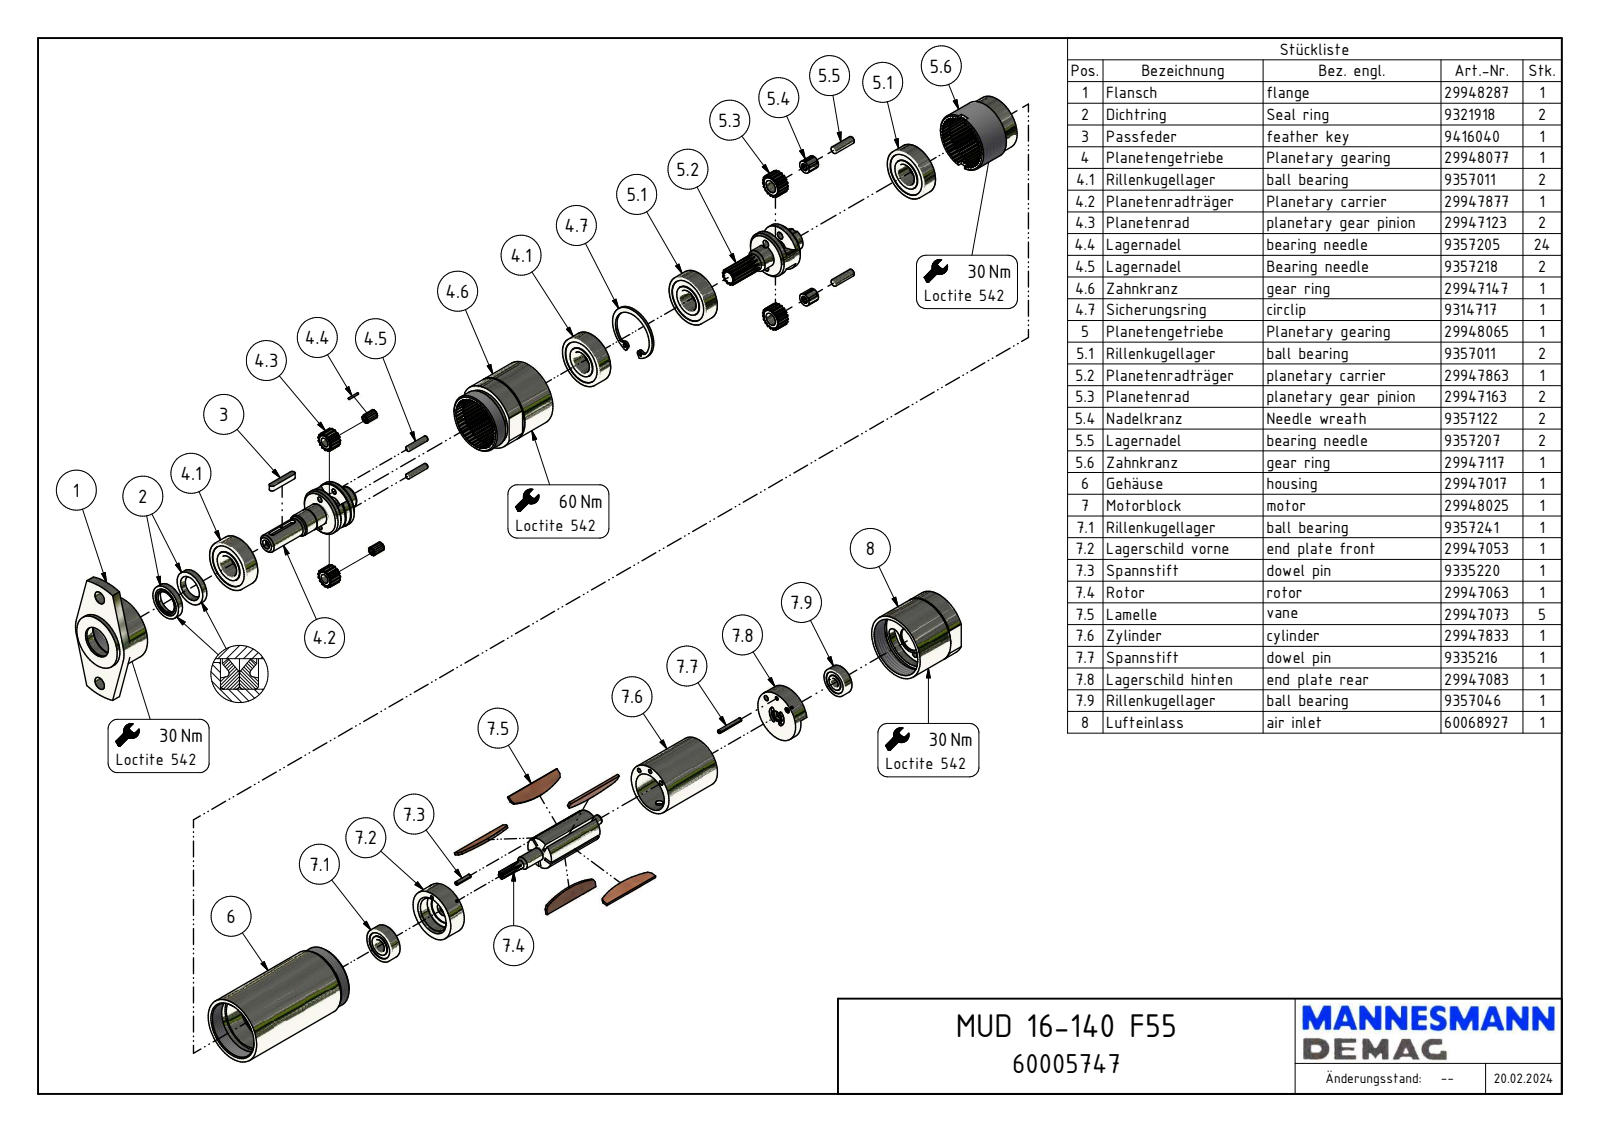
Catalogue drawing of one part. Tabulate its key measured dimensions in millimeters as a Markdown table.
| quantity | value |
| --- | --- |
| part name | MUD 16-140 F55_60005747 |
| STEP written by | Autodesk Inventor 2024 (AUTOMOTIVE_DESIGN) |
| units | millimeters |
| bodies | 1 solid, 139 faces (91 planar, 25 cylindrical, 23 other) |
| overall size | 169.7 × 70 × 36 |
| volume | 150 527 mm³ |
| surface area | 22 719 mm² |
| round holes (diameter × count) | 7 × 2, 8.57 × 2, 3.24 × 1, 11.45 × 1, 17 × 1 |
| round bosses / shafts (diameter × count) | 36 × 1, 34.99 × 1, 30 × 1, 11.95 × 1, 10 × 1, 9.8 × 1 |
| partial cylindrical surfaces (radius × count) | 1.5 × 2, 35 × 1 |
| main face-to-face distances | 5, 143.2, 138.2, 2, 7, 145.2, 33, 135.7, 133.7, 128.7 |
| hole center spacings | 11.1, 17.92, 22.85, 27.5, 35.17, 9, 18, 18.5 |
